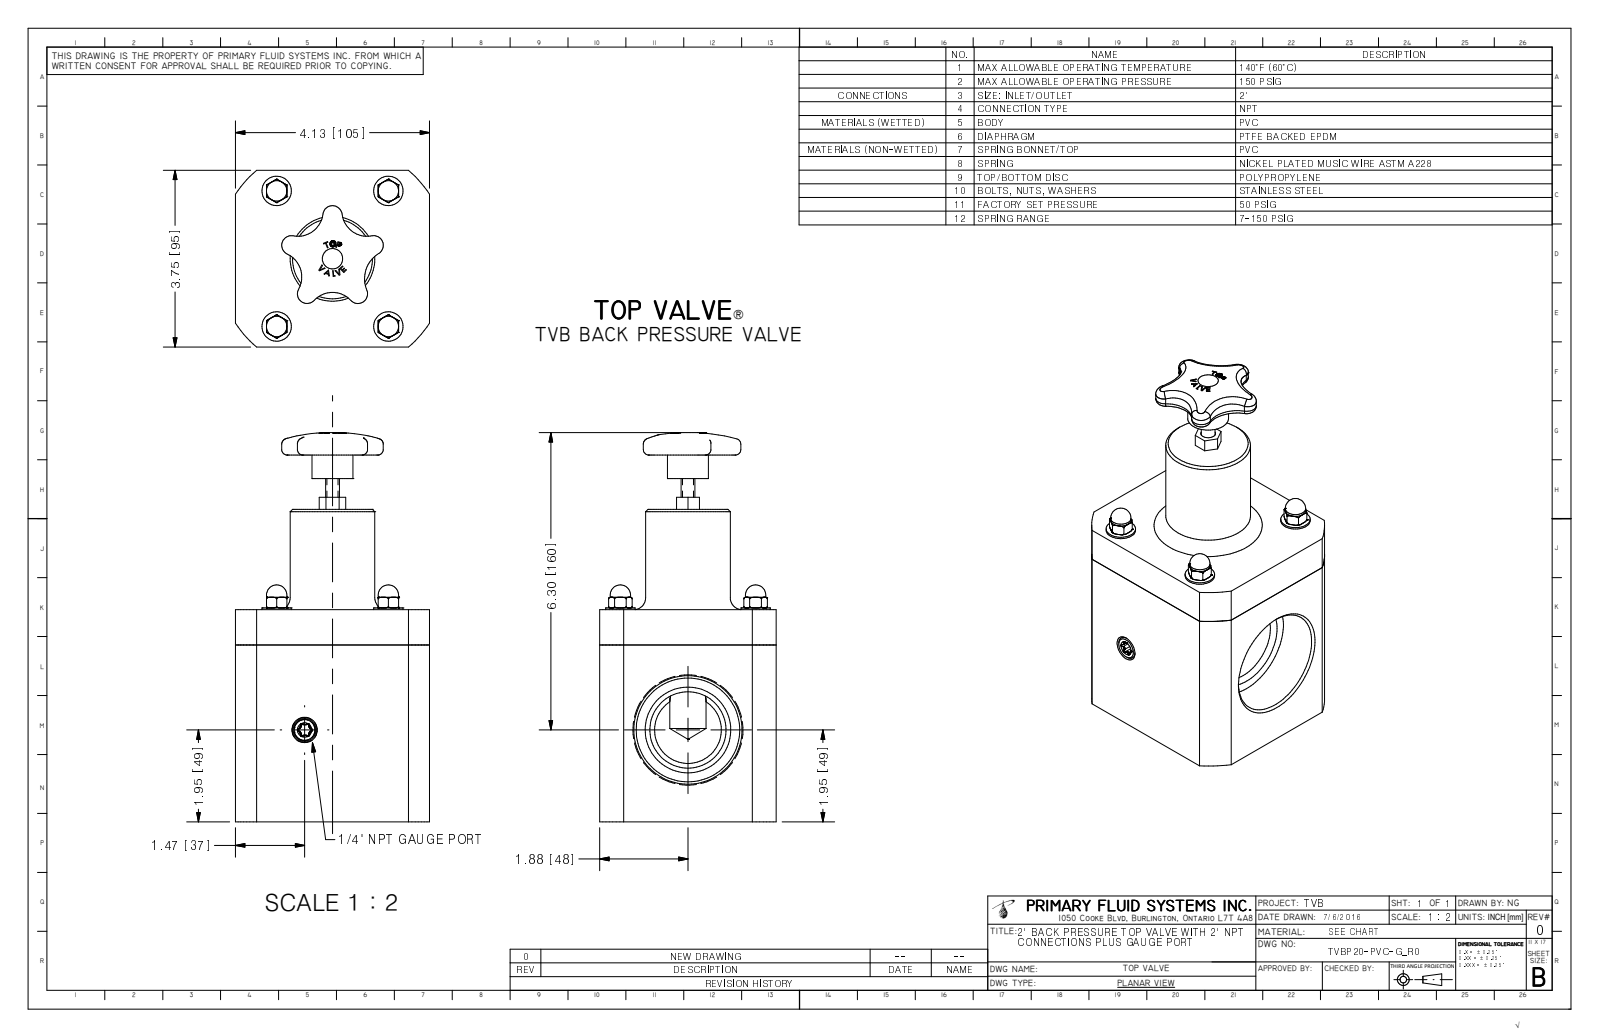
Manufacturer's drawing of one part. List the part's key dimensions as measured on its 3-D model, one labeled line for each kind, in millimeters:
Part name (STEP PRODUCT): TVBP20-PVC-G_R0
STEP written by: Autodesk Inventor 2009 (AUTOMOTIVE_DESIGN)
Units: millimetres
Bodies: 1 solid, 359 faces (152 planar, 51 cylindrical, 156 other)
Overall size (bounding box): 209.6 × 104.8 × 95.3
Volume: 1 112 000 mm³ · Surface area: 87 610 mm²
Round holes (diameter × count): ⌀4.4 ×4, ⌀55.9 ×1
Round bosses / shafts (diameter × count): ⌀15.9 ×4, ⌀11 ×4, ⌀9.5 ×4, ⌀45.7 ×1, ⌀22.1 ×1, ⌀7.4 ×1
Partial cylindrical surfaces — rounded edges, fillets, slot ends (radius × count): R0.7 ×6, R2.2 ×5, R5.2 ×5, R13.6 ×4, R16.7 ×4, R15.9 ×1, R18.9 ×1, R62.9 ×1
Main face-to-face distances: 95.3, 114.3, 104.8, 22.9, 81.9, 59.1, 168.3, 54, 11, 115.2
Hole centre spacings: 60.3, 73, 94.7
